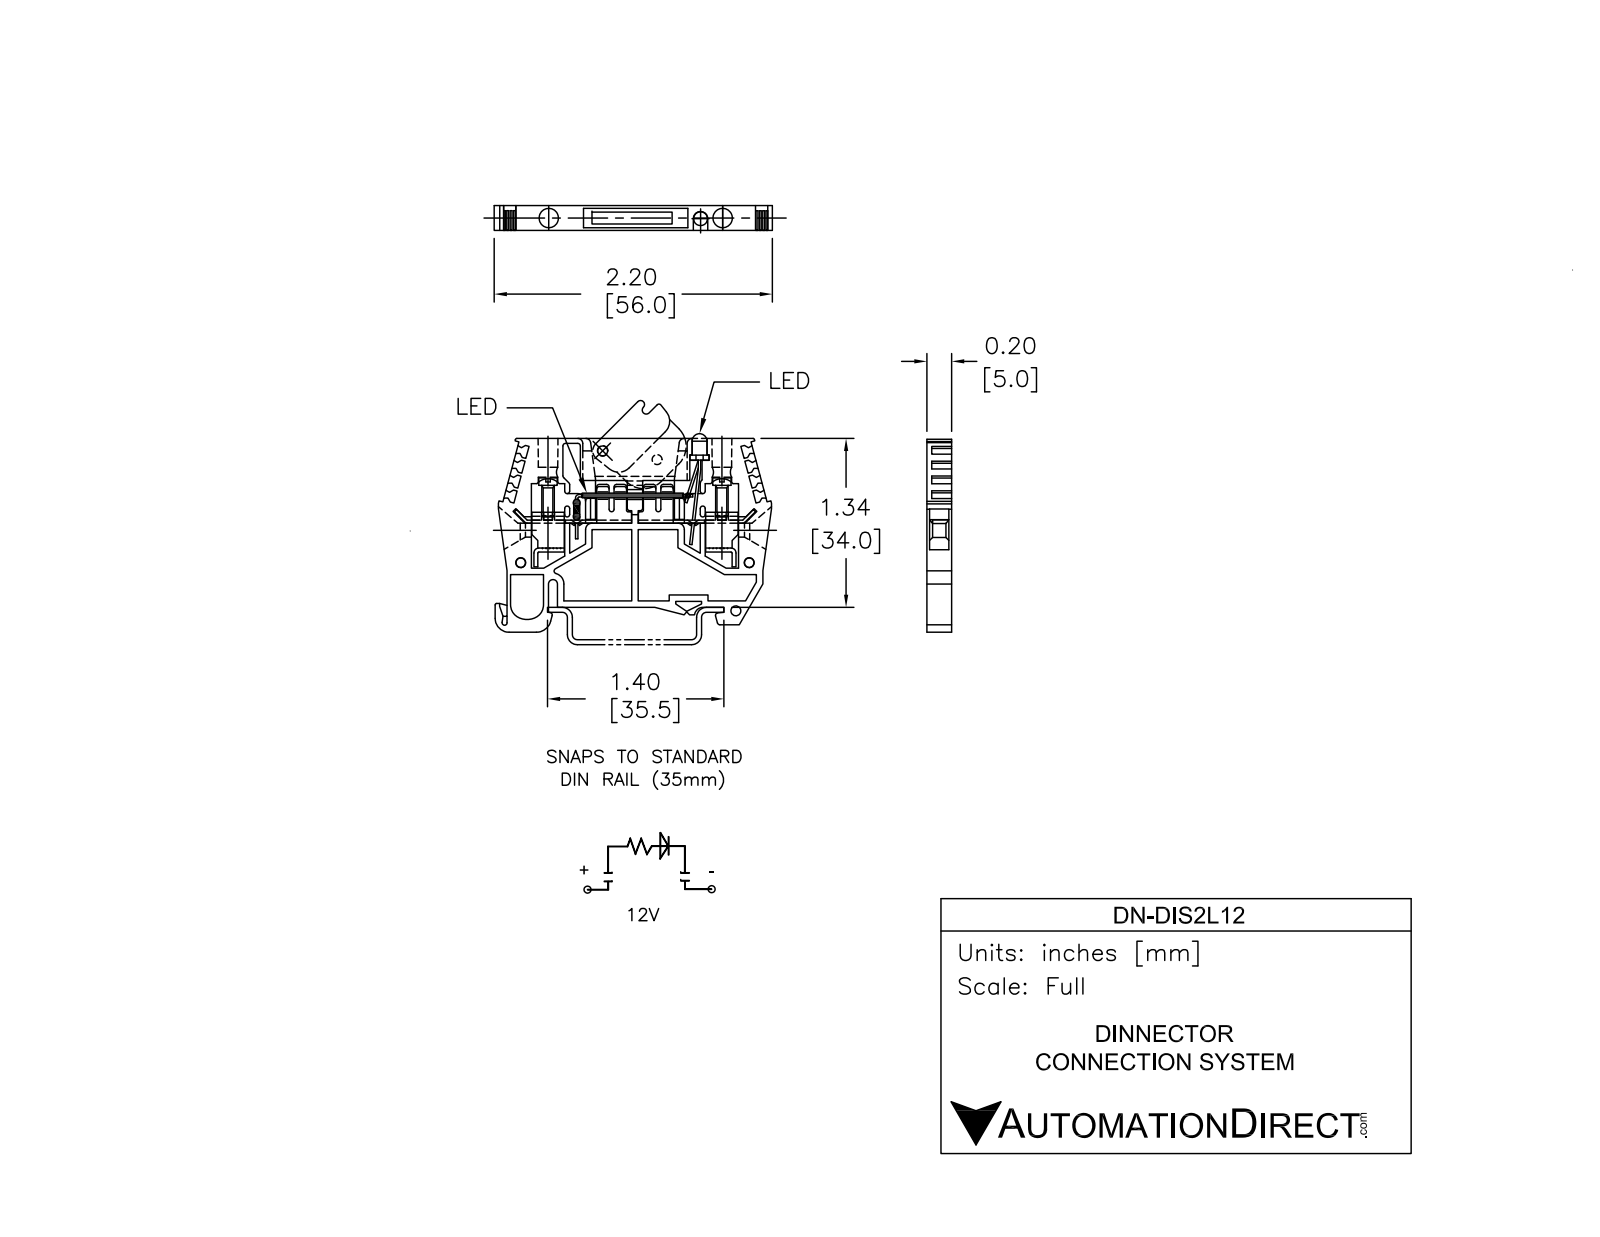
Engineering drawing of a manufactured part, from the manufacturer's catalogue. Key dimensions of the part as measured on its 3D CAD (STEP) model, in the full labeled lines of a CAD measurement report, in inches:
Part name (STEP PRODUCT): 435K0001; 20621_1; 4358004_DN-D1S2L12; 4258000_DN-QFE2_1
STEP written by: SolidWorks 2013 (AUTOMOTIVE_DESIGN)
Units: inches
Bodies: 3 solids, 392 faces (222 planar, 112 cylindrical, 58 other)
Overall size (bounding box): 2.191 × 1.559 × 0.234
Volume: 0.487 in³ · Surface area: 10.2 in²
Round holes (diameter × count): ⌀0.079 ×4, ⌀0.161 ×2
Round bosses / shafts (diameter × count): ⌀0.012 ×10, ⌀0.157 ×1, ⌀0.118 ×1, ⌀0.079 ×1
Partial cylindrical surfaces — rounded edges, fillets, slot ends (radius × count): R0.02 ×22, R0.118 ×7, R0.039 ×3, R0.031 ×2, R0.197 ×2, R0.035 ×1, R0.041 ×1, R0.067 ×1
Main face-to-face distances: 0.197, 0.087, 0.024, 1.339, 0.175, 0.022, 0.112, 0.089, 0.039, 0.154
Hole centre spacings: 1.05, 0.396, 1.214, 1.378, 1.747, 1.811
